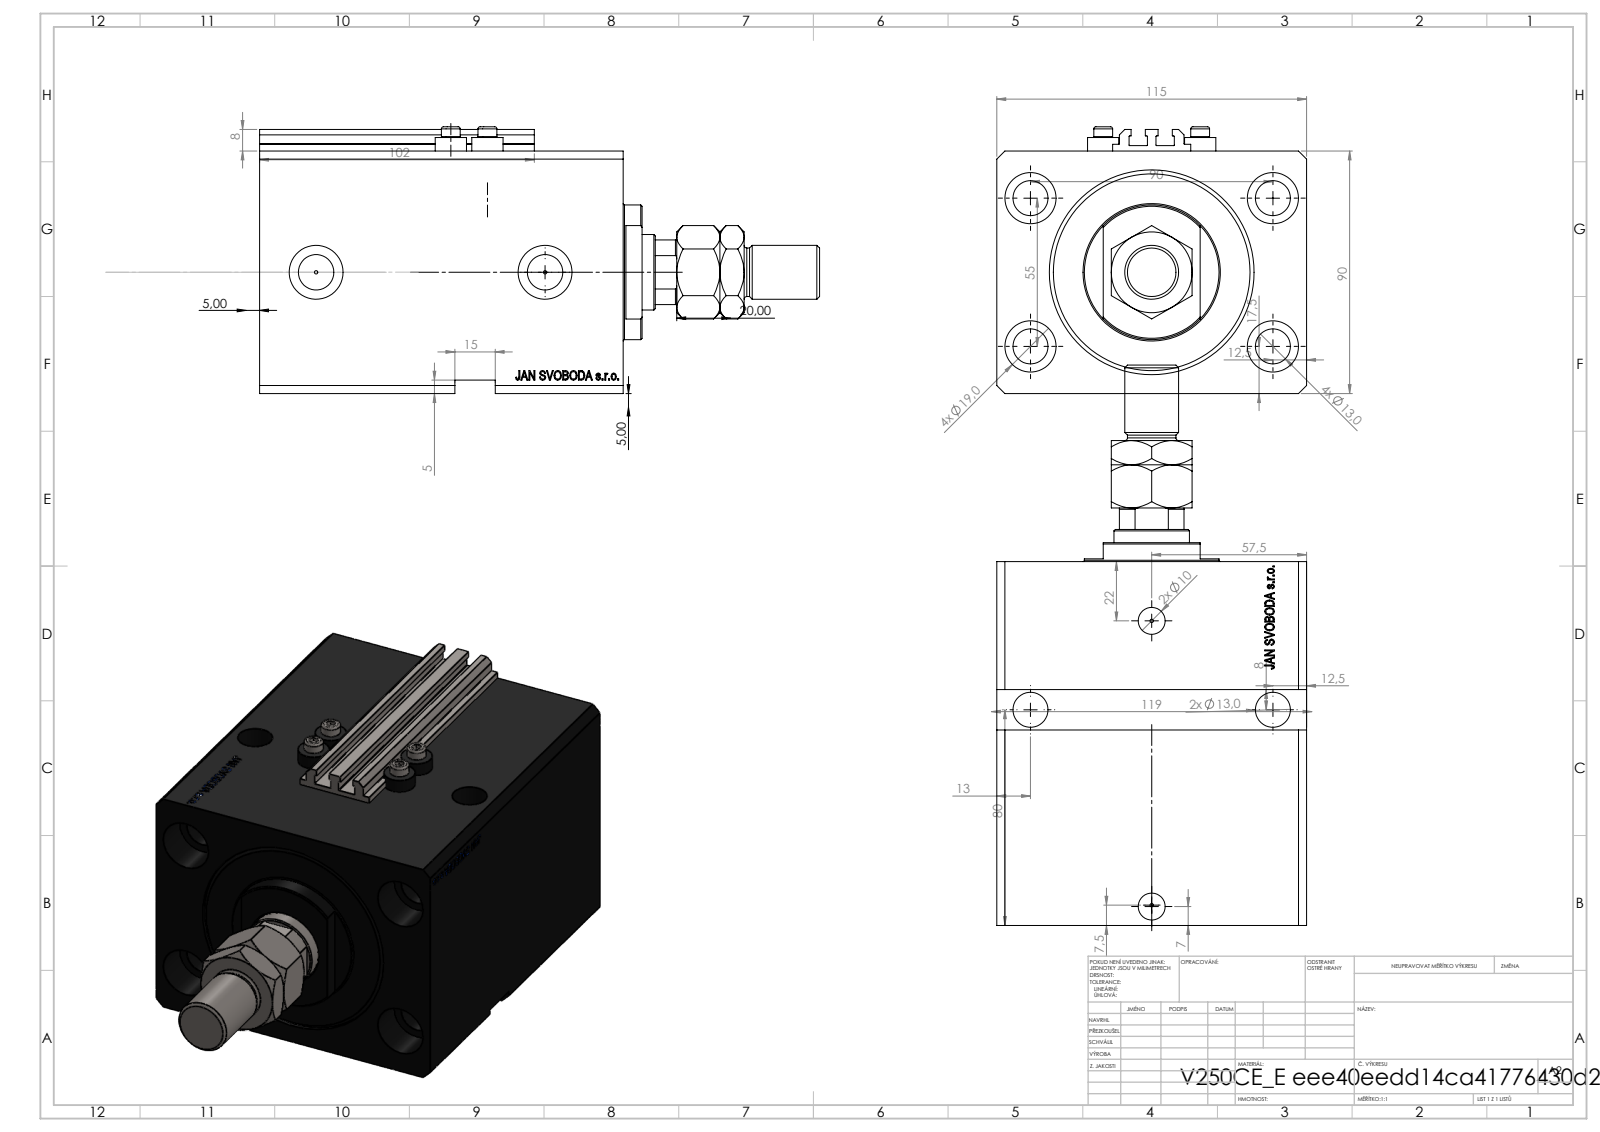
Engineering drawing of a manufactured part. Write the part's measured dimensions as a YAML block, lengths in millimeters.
part_name: "MTA; V250CE_C_VCP; V250CE_VC_E; ALLEN BOLT V250CE (+1 more)"
step_written_by: "SolidWorks 2019 (CONFIG_CONTROL_DESIGN)"
units: millimeters
bodies: {solids: 9, faces: 1176, planar: 558, cylindrical: 150, other: 468}
overall_size: [208, 115, 99]
volume: 1187000
surface_area: 192513
round_holes:
  - {diameter: 13, count: 8}
  - {diameter: 1.25, count: 4}
  - {diameter: 4, count: 4}
  - {diameter: 19, count: 4}
  - {diameter: 10, count: 2}
  - {diameter: 13.16, count: 2}
  - {diameter: 20, count: 2}
  - {diameter: 18.5, count: 1}
  - {diameter: 28, count: 1}
  - {diameter: 63, count: 1}
  - {diameter: 76, count: 1}
round_bosses_or_shafts:
  - {diameter: 11.6, count: 4}
  - {diameter: 7, count: 4}
  - {diameter: 50, count: 1}
  - {diameter: 20, count: 1}
  - {diameter: 18, count: 1}
partial_cylinders:
  - {radius: 0.2, count: 10}
  - {radius: 13.5, count: 1}
face_to_face_distances: [115, 90, 20, 135, 17.9, 117.1, 97.1, 65, 13, 47.1]
hole_center_spacings: [52.74, 55.8, 85.76, 90, 13.6, 27.39, 28.46, 33.62]
